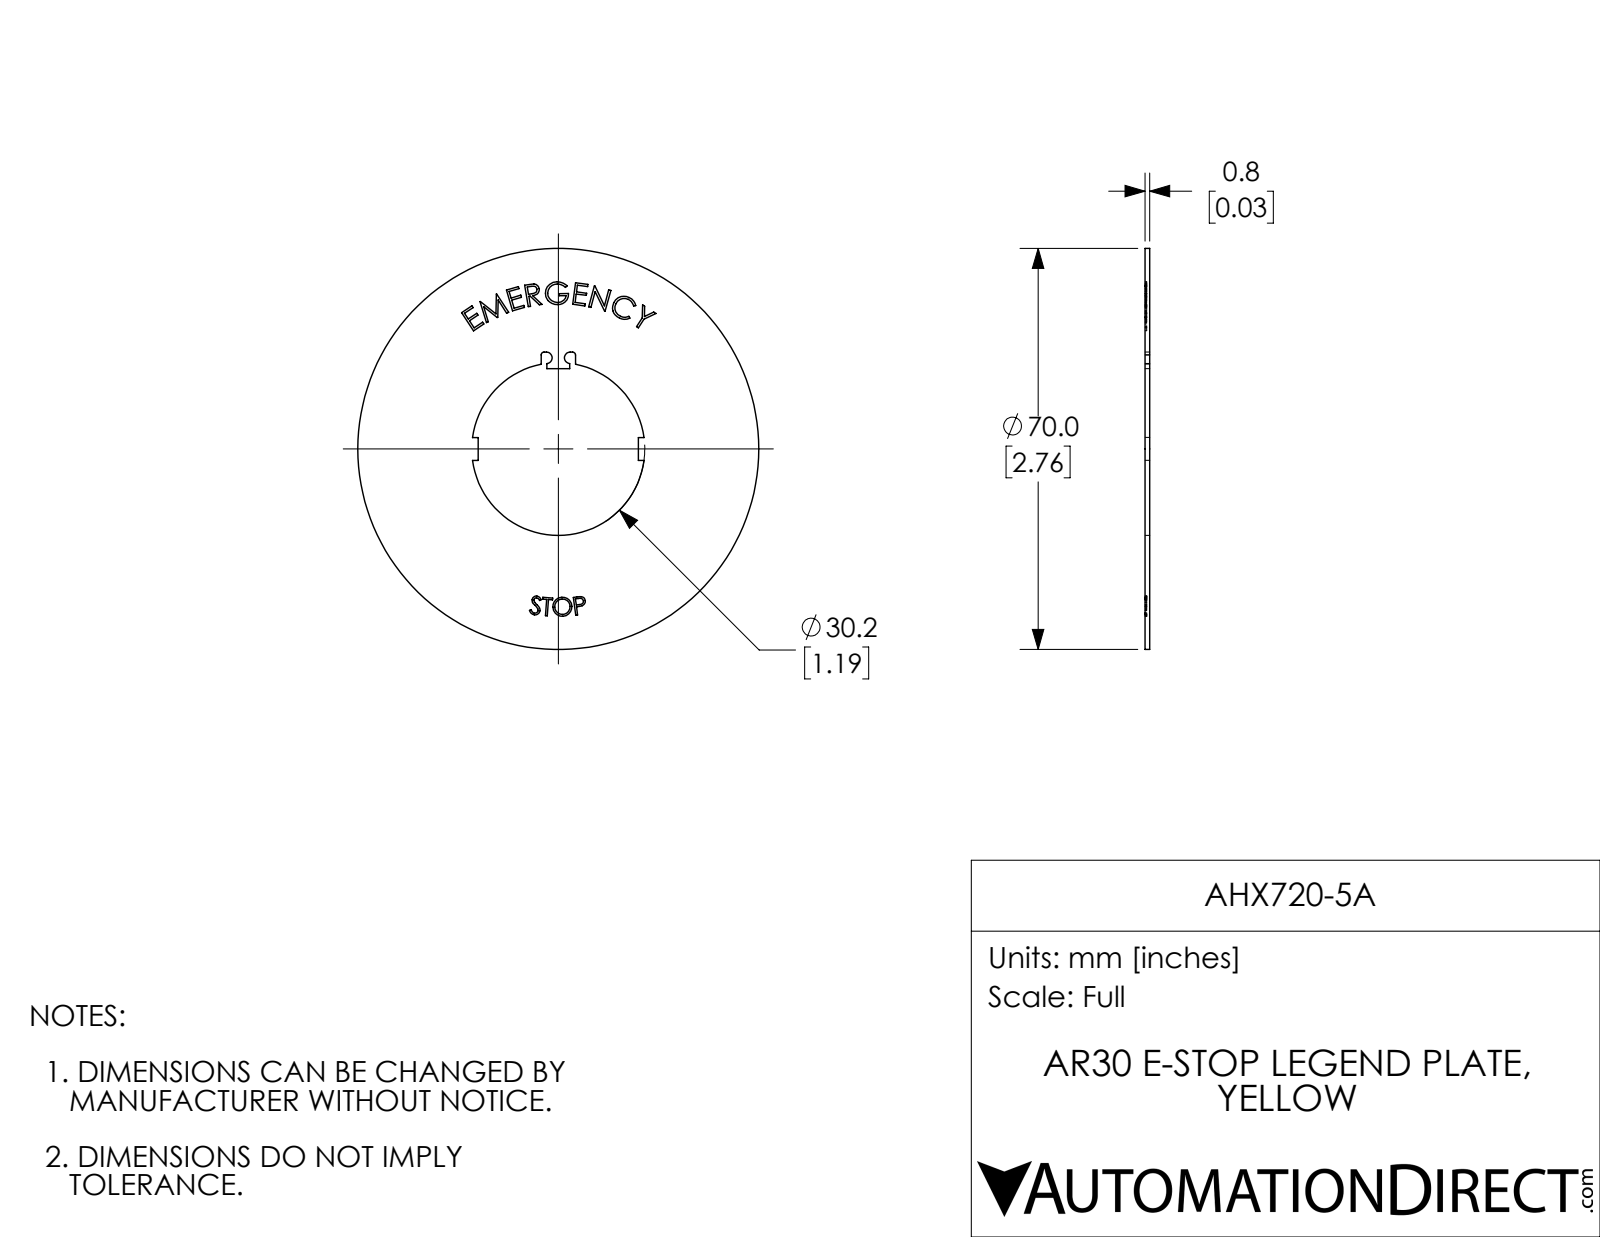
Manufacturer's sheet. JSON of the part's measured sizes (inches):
{"part_name": "AHX720-5A", "step_written_by": "SolidWorks 2017 (AUTOMOTIVE_DESIGN)", "units": "inches", "bodies": {"solids": 1, "faces": 196, "planar": 134, "cylindrical": 10, "other": 52}, "overall_size": [2.756, 2.756, 0.031], "volume_in3": 0.153, "surface_area_in2": 10.23, "round_holes": [[1.189, 1]], "round_bosses_or_shafts": [[2.756, 1]], "partial_cylinders_radius": [[0.02, 2], [0.039, 2]], "face_to_face_distances": [0.031, 0.022, 0.015, 0.015, 1.102, 0.63, 0.472, 0.061, 0.433, 0.669]}
